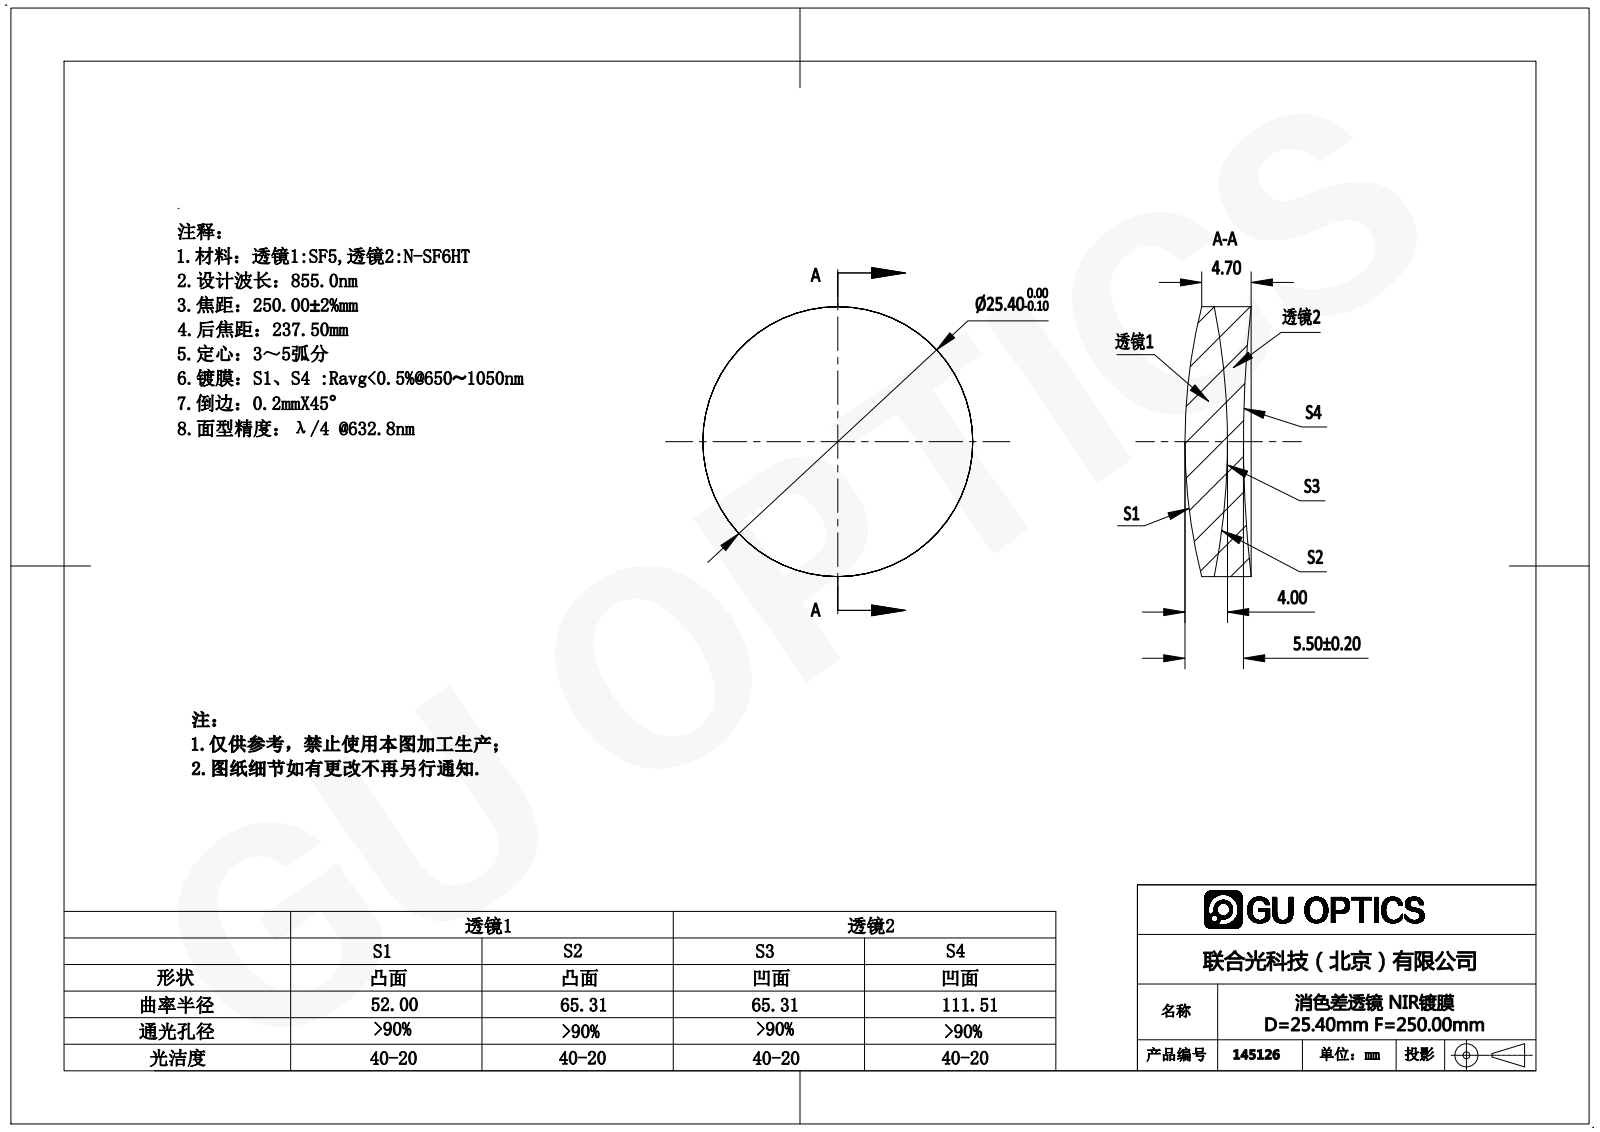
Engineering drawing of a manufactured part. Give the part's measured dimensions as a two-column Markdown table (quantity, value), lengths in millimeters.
| quantity | value |
| --- | --- |
| part name | 145126 |
| STEP written by | SolidWorks 2016 (AUTOMOTIVE_DESIGN) |
| units | millimeters |
| bodies | 2 solids, 12 faces (0 planar, 4 cylindrical, 8 other) |
| overall size | 25.4 × 25.4 × 6.23 |
| volume | 2 574 mm³ |
| surface area | 2 417 mm² |
| round bosses / shafts (diameter × count) | 25.4 × 1 |
